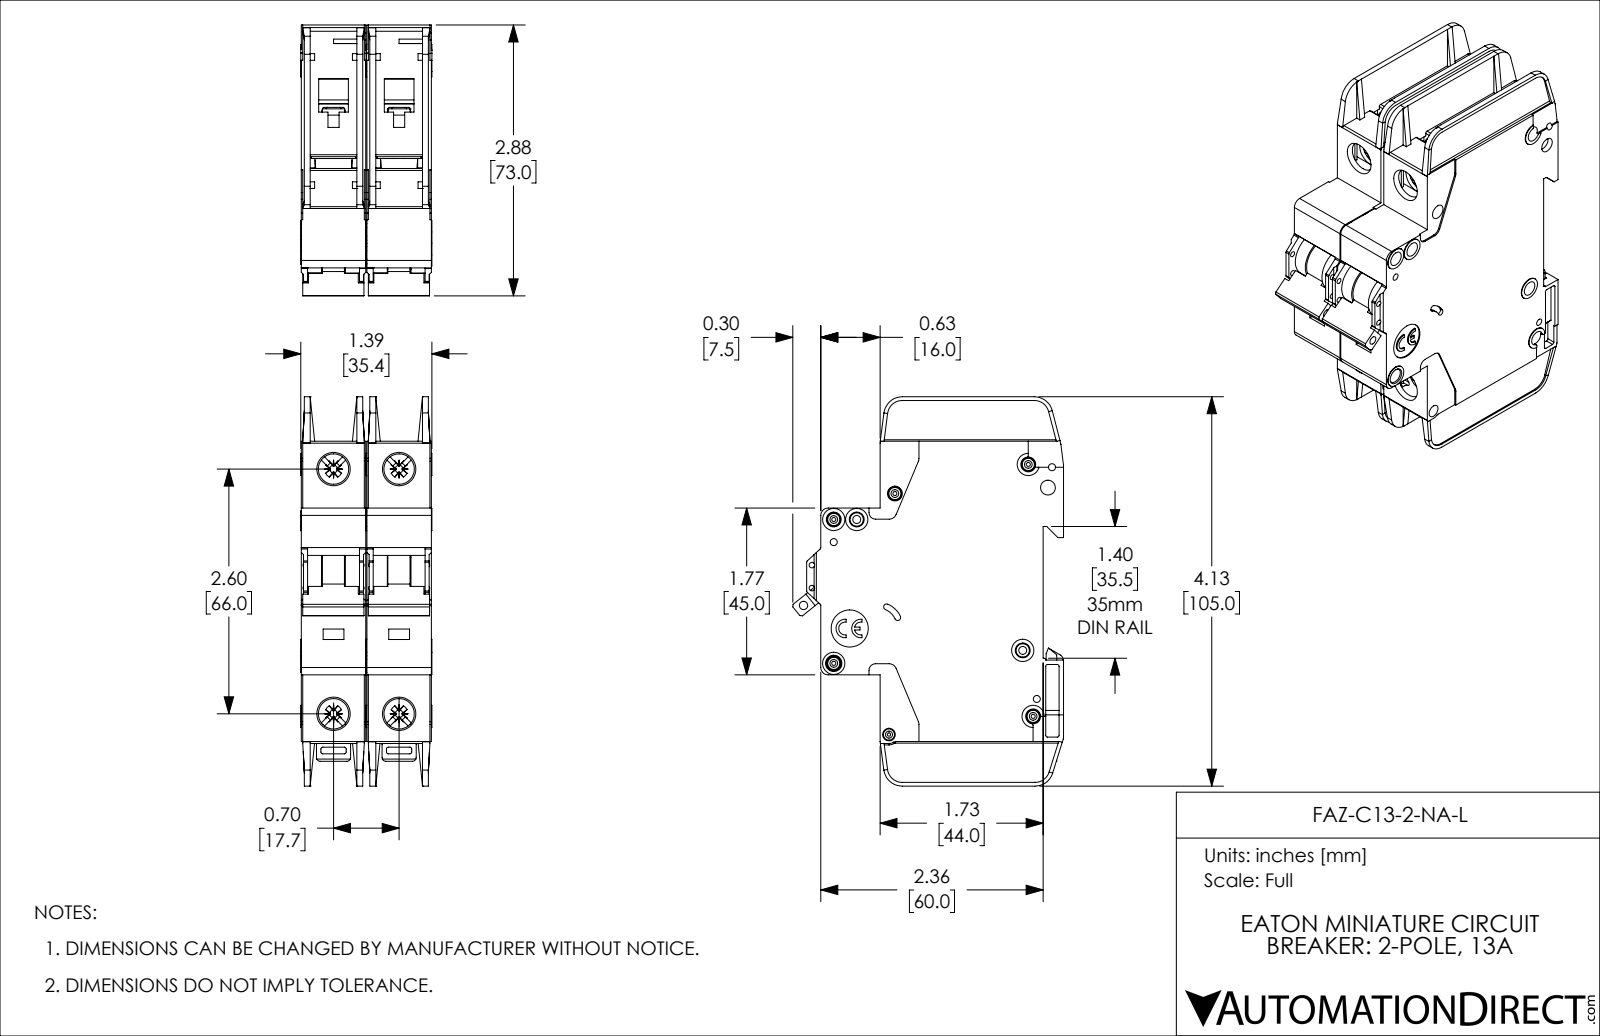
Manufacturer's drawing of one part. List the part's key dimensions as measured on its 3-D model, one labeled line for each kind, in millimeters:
Part name (STEP PRODUCT): FAZ-C13-2-NA-L
STEP written by: SolidWorks 2019 (AUTOMOTIVE_DESIGN)
Units: millimetres
Bodies: 2 solids, 2254 faces (1342 planar, 714 cylindrical, 198 other)
Overall size (bounding box): 105 × 73.1 × 35.4
Volume: 153 500 mm³ · Surface area: 52 910 mm²
Round holes (diameter × count): ⌀4 ×8, ⌀1.1 ×5, ⌀1.9 ×4, ⌀8.2 ×4, ⌀1.5 ×2, ⌀2.2 ×2, ⌀0.9 ×1, ⌀2.3 ×1, ⌀2.5 ×1, ⌀3.4 ×1, ⌀10 ×1
Round bosses / shafts (diameter × count): ⌀3.3 ×5, ⌀6 ×4, ⌀3 ×3, ⌀2.5 ×2
Partial cylindrical surfaces — rounded edges, fillets, slot ends (radius × count): R0.5 ×57, R0.4 ×20, R1 ×14, R2 ×10, R1.1 ×8, R0.2 ×5, R5 ×5, R0.3 ×4
Main face-to-face distances: 17.7, 1.2, 17.4, 15, 2.4, 16.2, 13.8, 35.1, 18.9, 16.5
Hole centre spacings: 6.2, 13.6, 17.7, 22.1, 66, 68.3, 4.8, 5.1
